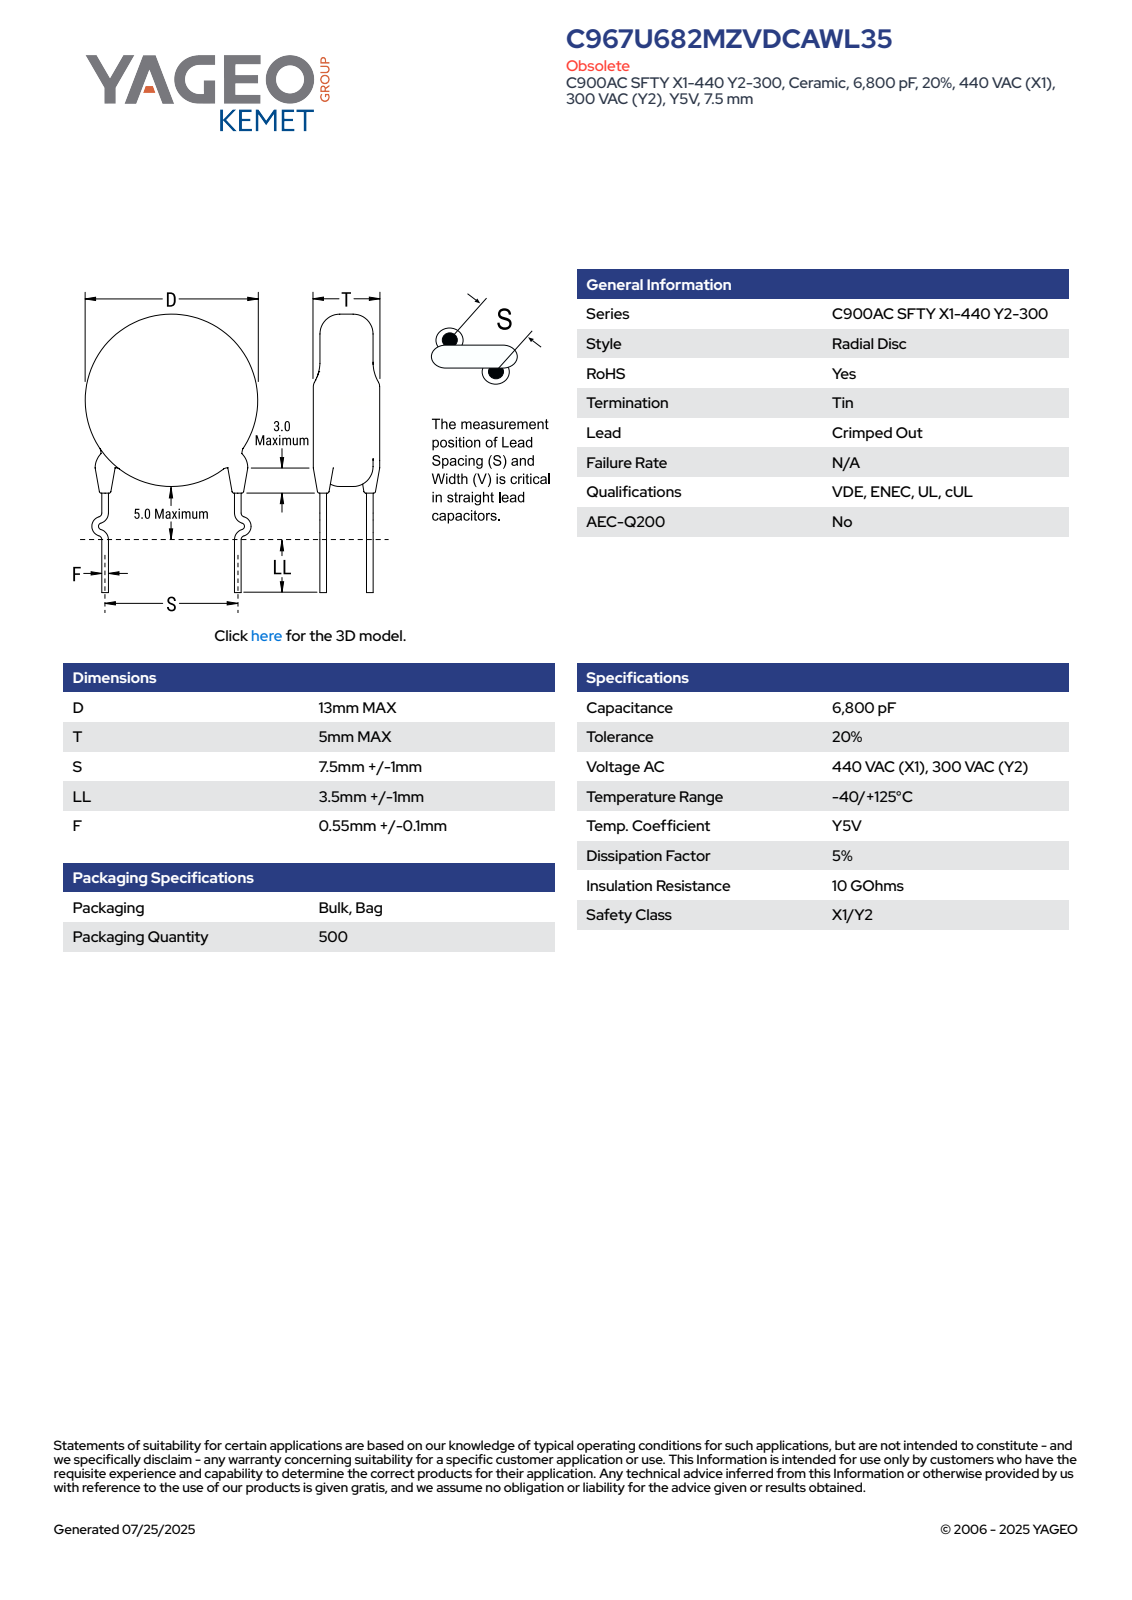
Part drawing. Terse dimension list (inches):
name: CCD_KCOC900_D13T5S7.5LL4.5F0.55
written by: SolidWorks 2014 (AUTOMOTIVE_DESIGN)
unit: in
bodies: 4 solids, 85 faces (63 planar, 6 cylindrical, 16 other)
size: 0.886 × 0.512 × 0.197
volume: 0.04 in³; area: 0.778 in²
bosses: 2× ⌀0.047, 1× ⌀0.512
face distances: 0.197, 0.283, 0.23, 0.053, 0.015, 0.013, 0.043, 0.217, 0.11, 0.158
